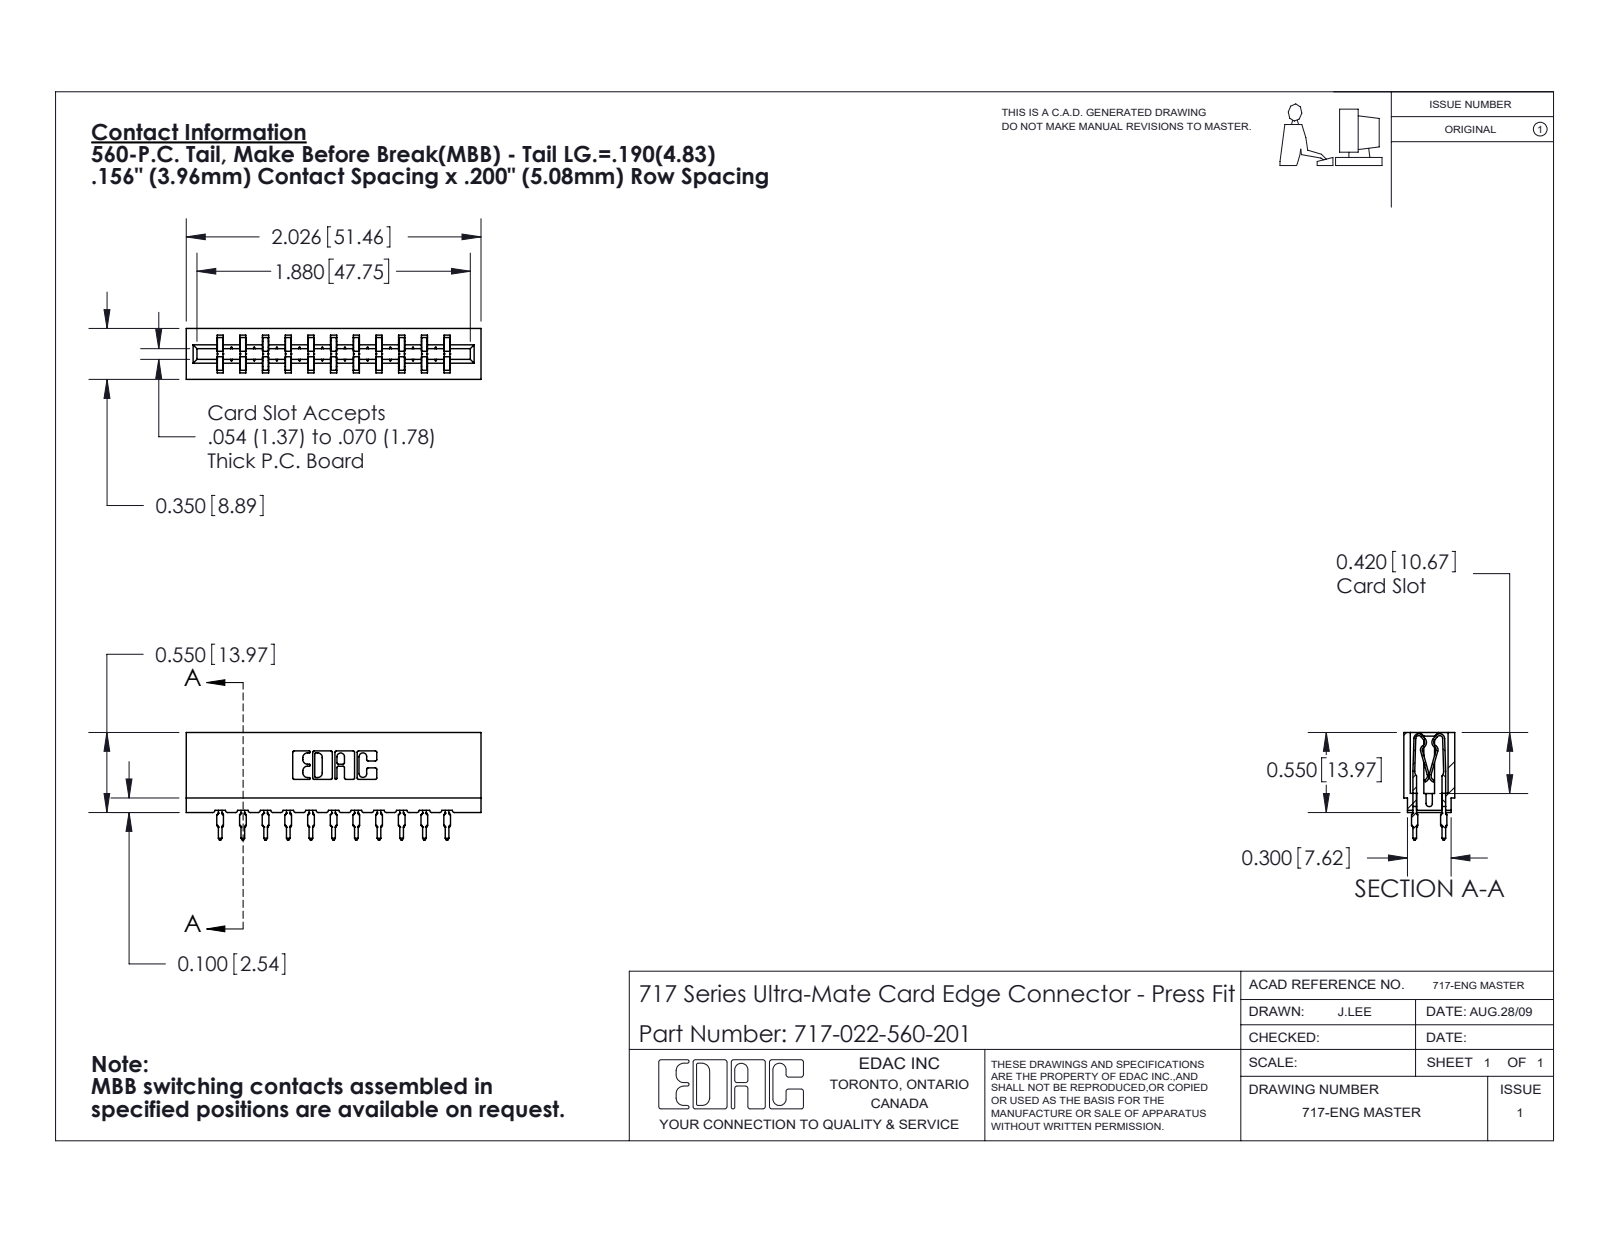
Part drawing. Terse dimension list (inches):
name: 717 Part_Insulator Option - 06; 745-292-001_560; 717-022-560-201
written by: SolidWorks 2020 (CONFIG_CONTROL_DESIGN)
unit: in
bodies: 23 solids, 2272 faces (1187 planar, 513 cylindrical, 572 other)
size: 2.026 × 0.739 × 0.35
volume: 0.285 in³; area: 11.02 in²
rounds: 44× R0.021, 22× R0.01, 22× R0.015, 8× R0.005, 8× R0.011, 6× R0.007, 6× R0.031, 3× R0.026
face distances: 0.212, 0.156, 0.138, 0.468, 0.624, 0.35, 0.312, 0.198, 0.312, 0.042
